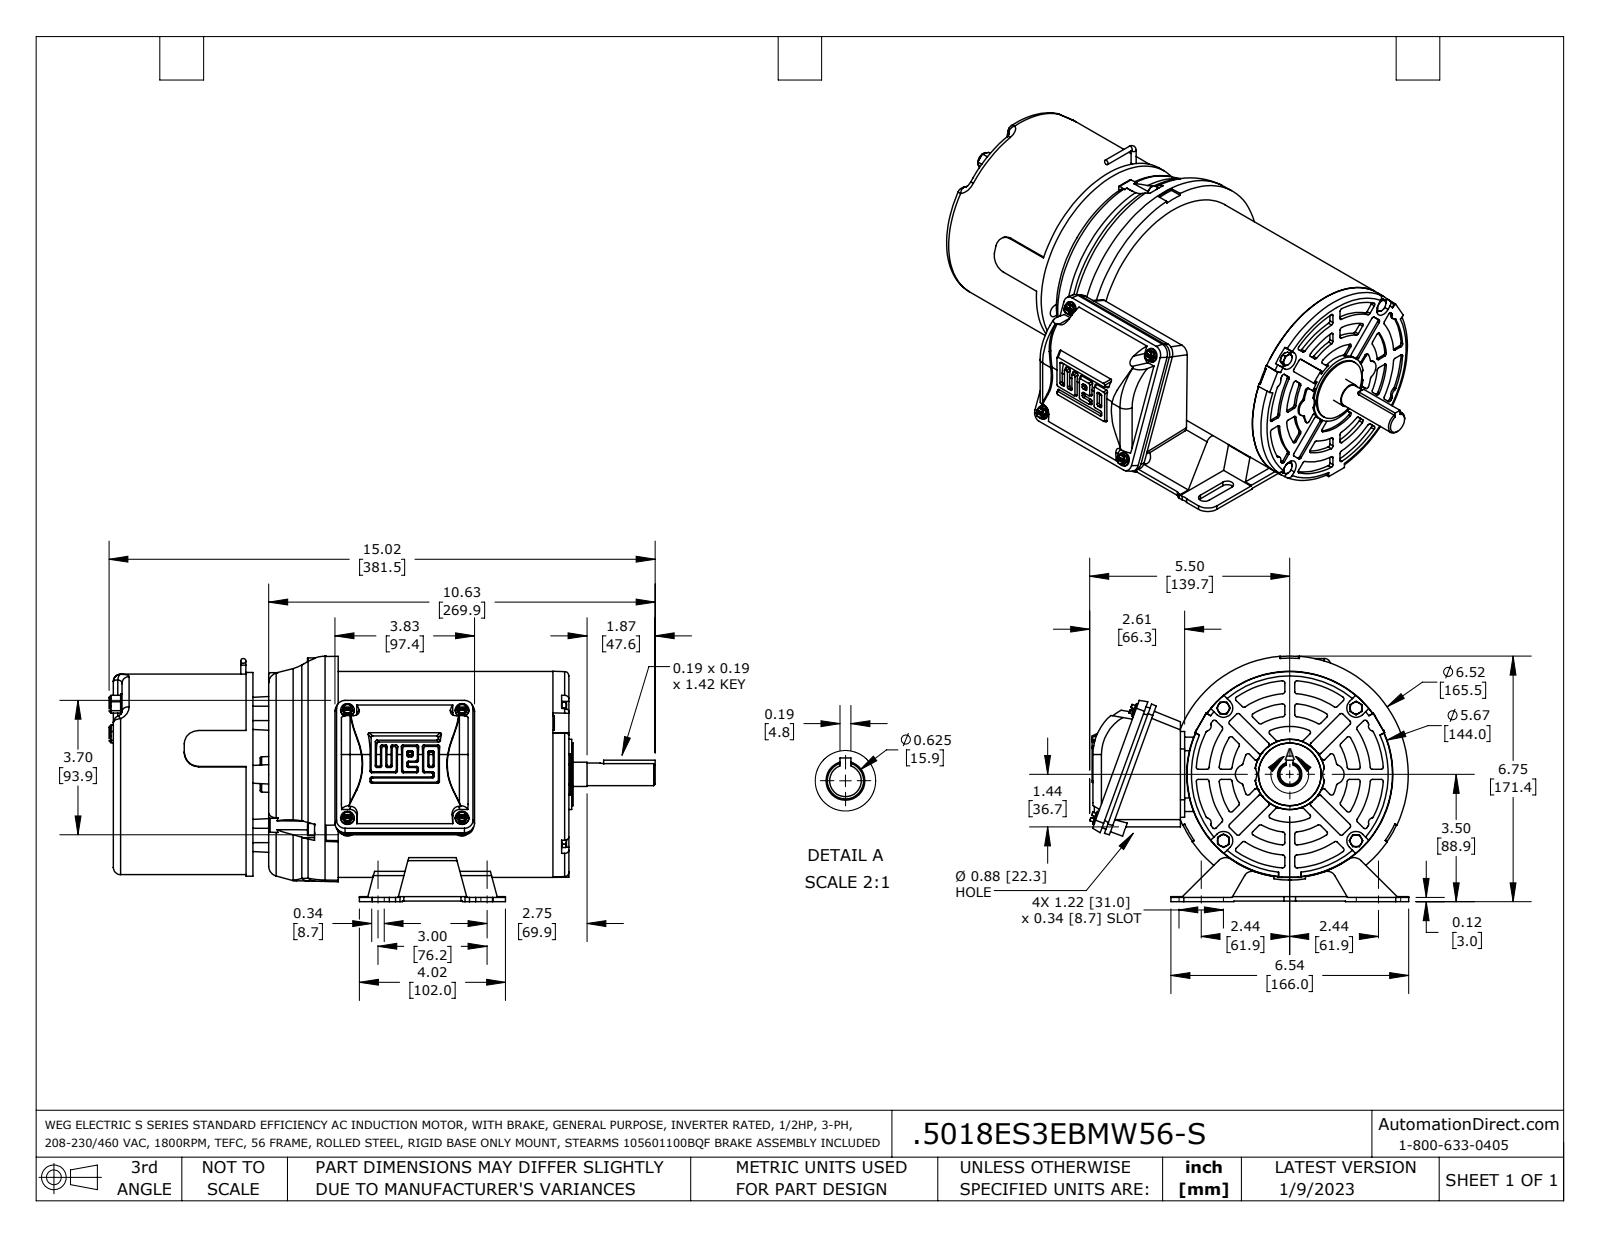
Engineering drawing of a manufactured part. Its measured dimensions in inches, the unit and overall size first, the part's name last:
Units: inches
Overall size (bounding box): 15.018 × 8.769 × 6.75
Round holes (diameter × count): ⌀0.236 ×4, ⌀0.25 ×2, ⌀0.28 ×2, ⌀0.37 ×2, ⌀0.5 ×1, ⌀3 ×1, ⌀5.157 ×1
Round bosses / shafts (diameter × count): ⌀0.374 ×4, ⌀0.187 ×4, ⌀0.335 ×3, ⌀0.197 ×3, ⌀0.551 ×2, ⌀0.437 ×2, ⌀0.138 ×2, ⌀5.659 ×1
Partial cylindrical surfaces — rounded edges, fillets, slot ends (radius × count): R0.059 ×92, R0.047 ×38, R0.197 ×15, R0.02 ×10, R0.171 ×8, R0.205 ×8, R0.276 ×8, R0.138 ×4
Main face-to-face distances: 5.906, 0.571, 6.476, 1.772, 7.52, 1.043, 1.614, 0.728, 2.343, 8.248
Hole centre spacings: 3.15, 0.718, 1.874, 2.227, 2.34, 3.149, 4.178, 4.454
Volume: 315.4 in³ · Surface area: 695.1 in²
Bodies: 16 solids, 1498 faces (582 planar, 422 cylindrical, 494 other)
Part name (STEP PRODUCT): W56_3PH_TEFC_BM_15004 coord fxt
STEP written by: SolidWorks 2021 (AUTOMOTIVE_DESIGN)
